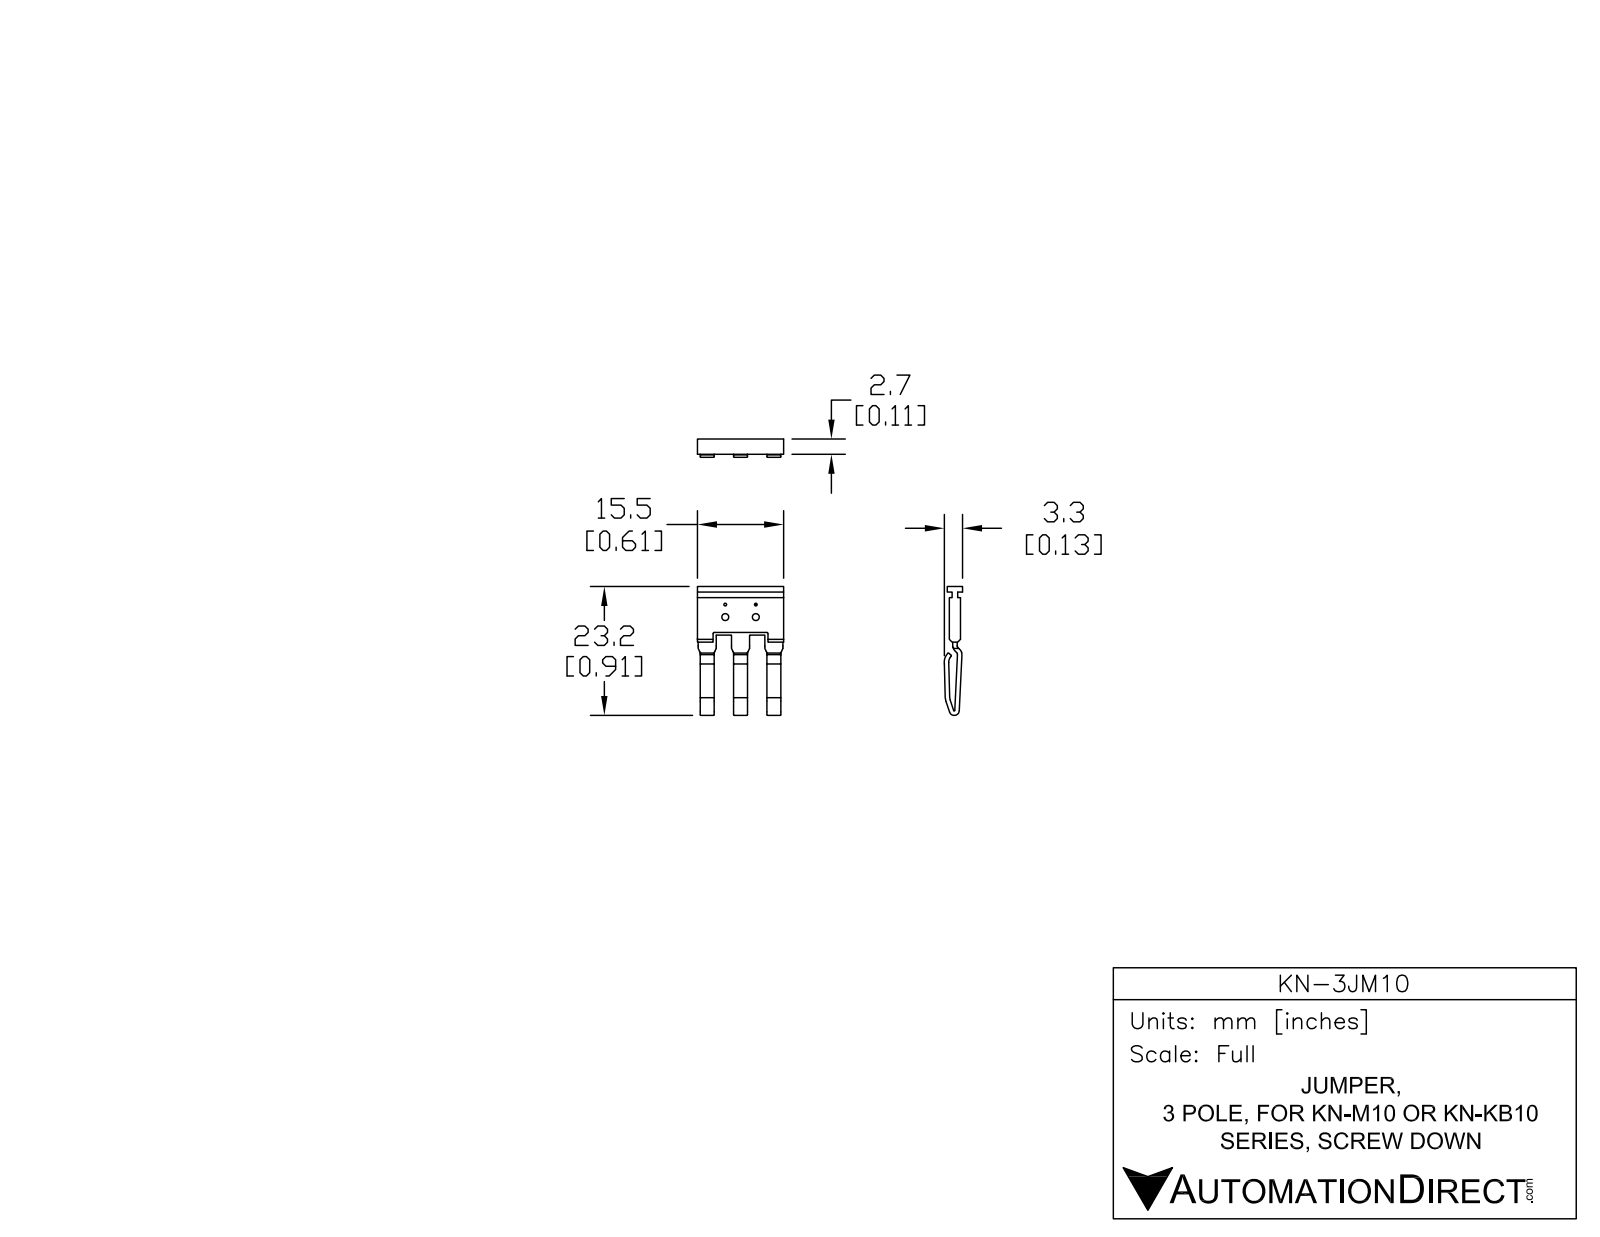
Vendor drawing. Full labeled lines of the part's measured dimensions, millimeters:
Part name (STEP PRODUCT): KN-3JM10
STEP written by: SolidWorks 2014 (AUTOMOTIVE_DESIGN)
Units: millimetres
Bodies: 1 solid, 319 faces (84 planar, 130 cylindrical, 105 other)
Overall size (bounding box): 23.19 × 15.5 × 3.3
Volume: 422 mm³ · Surface area: 946 mm²
Round holes (diameter × count): ⌀0.5 ×2, ⌀1.25 ×2
Partial cylindrical surfaces — rounded edges, fillets, slot ends (radius × count): R0.12 ×74, R0.25 ×2, R0.6 ×2, R1.4 ×2, R1.6 ×2, R2.4 ×2, R0.1 ×1, R0.9 ×1
Main face-to-face distances: 2, 0.8, 0.5, 1, 6, 2.5, 0.6, 1.4, 1.5, 0.9
Hole centre spacings: 2.25, 5.5, 5.94
